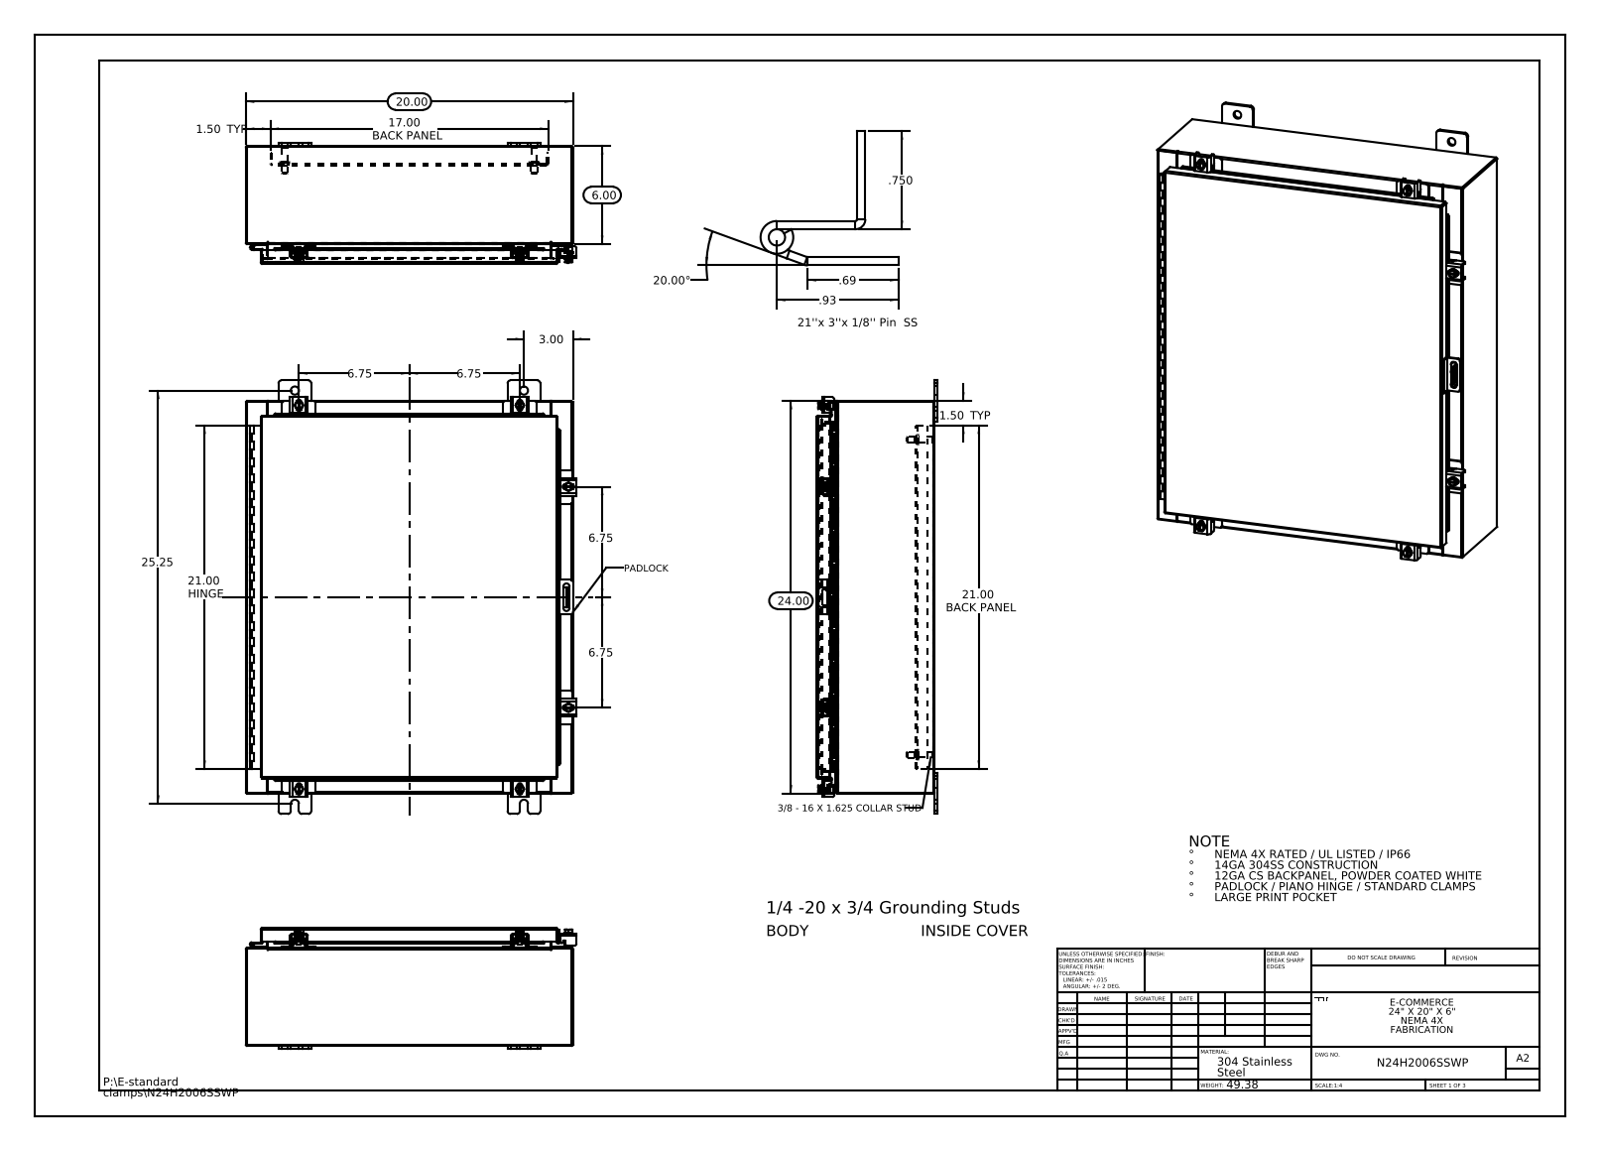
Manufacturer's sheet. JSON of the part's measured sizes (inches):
{"part_name": "N24H2006SSWP Bottom; N24H2006SSWP Hinge Enclosure Side2; N24H2006SSWP Backpanel; N24H2006SSWP 22104005_DEFAULT (+8 more)", "step_written_by": "SolidWorks 2013 (CONFIG_CONTROL_DESIGN)", "units": "inches", "bodies": {"solids": 47, "faces": 1709, "planar": 908, "cylindrical": 705, "other": 96}, "overall_size": [26.5, 20.211, 7.389], "volume_in3": 173.9, "surface_area_in2": 4361, "round_holes": [[0.5, 8], [0.213, 6], [0.26, 6], [0.125, 2], [0.125, 1]], "round_bosses_or_shafts": [[0.25, 7], [0.5, 6], [0.399, 6], [0.625, 4], [0.375, 4], [0.33, 4]], "partial_cylinders_radius": [[0.06, 30], [0.013, 25], [0.19, 24], [0.088, 21], [0.12, 12], [0.141, 12], [0.125, 10], [0.05, 9]], "face_to_face_distances": [0.075, 7.126, 7.201, 7.051, 0.104, 1, 1.075, 6.051, 6.126, 1.179], "hole_center_spacings": [21.369, 25.739, 13.5, 0.431, 0.934, 1.858, 2.275, 2.276]}
